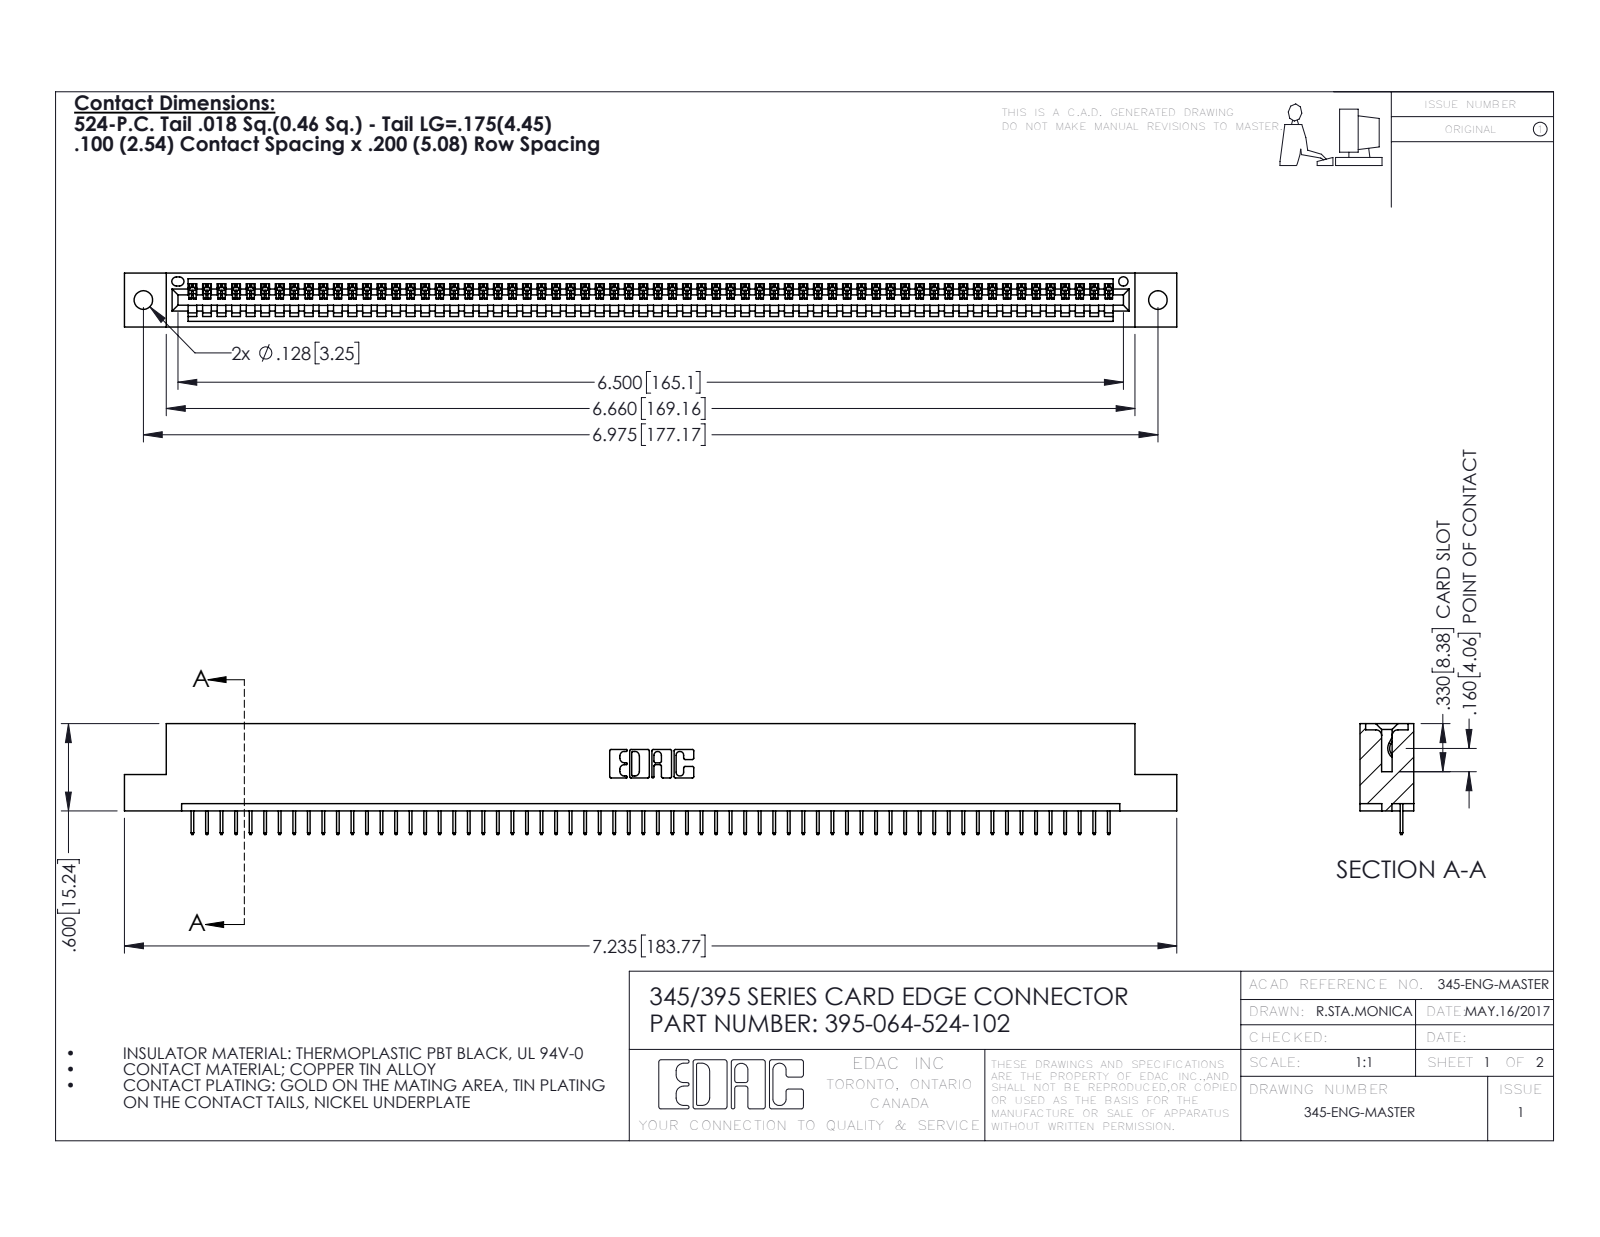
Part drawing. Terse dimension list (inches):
name: 345-292-001_345-293-124; 345 Part_Flush Mounting Lugs - 0.128 Dia; 395-064-524-102
written by: SolidWorks 2016 (CONFIG_CONTROL_DESIGN)
unit: in
bodies: 65 solids, 4094 faces (3024 planar, 1070 cylindrical, 0 other)
size: 7.235 × 0.762 × 0.37
volume: 1.058 in³; area: 34.52 in²
holes: 2× ⌀0.128, 1× ⌀0.064
rounds: 128× R0.006, 22× R0.01, 6× R0.007, 6× R0.031, 3× R0.026, 2× R0.031, 2× R0.04, 1× R0.014
face distances: 0.298, 0.072, 0.37, 0.2, 0.098, 0.272, 0.025, 0.225, 0.072, 0.149
hole spacings: 0.27, 6.739, 6.975
